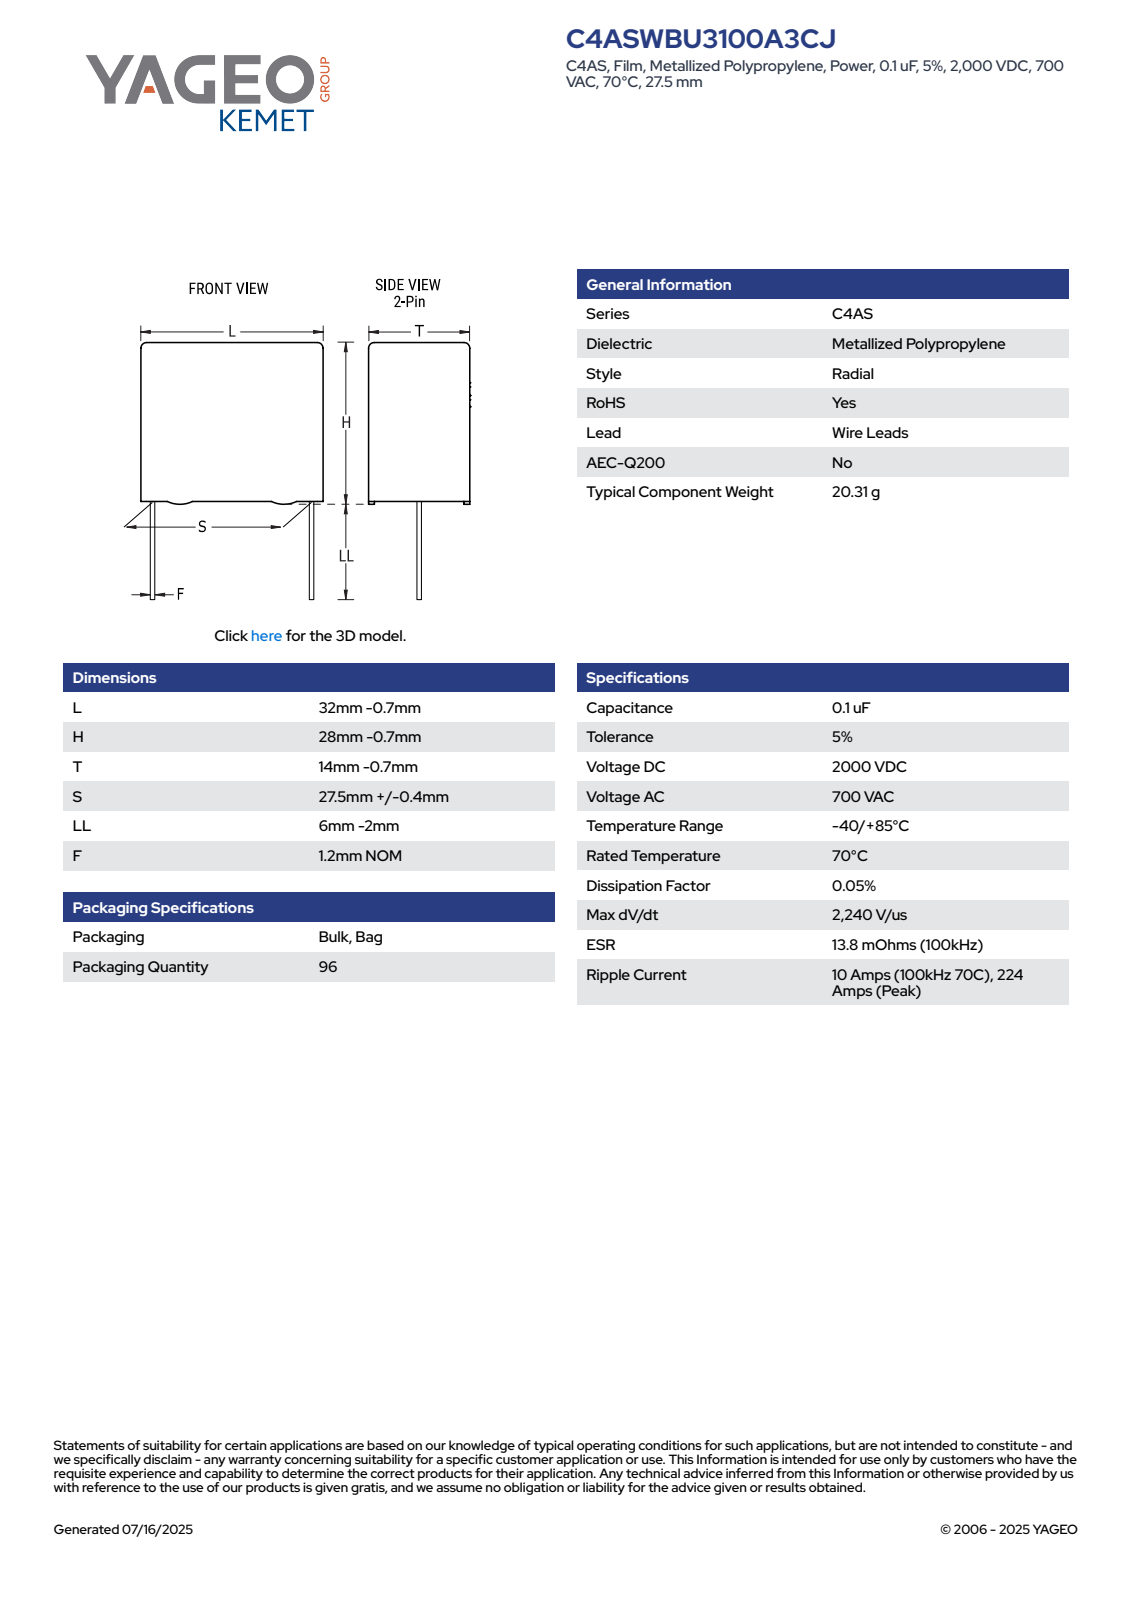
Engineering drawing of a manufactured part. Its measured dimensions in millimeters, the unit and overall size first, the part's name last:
Units: millimetres
Overall size (bounding box): 31.3 × 31.3 × 13.3
Round bosses / shafts (diameter × count): ⌀1.2 ×2
Partial cylindrical surfaces — rounded edges, fillets, slot ends (radius × count): R0.5 ×4
Main face-to-face distances: 13.3, 26.75, 31.3, 0.55, 27.3, 13.31, 0.76, 12.54, 0.77, 11.78
Volume: 11 151 mm³ · Surface area: 3 301 mm²
Bodies: 4 solids, 89 faces (81 planar, 8 cylindrical, 0 other)
Part name (STEP PRODUCT): CFP_RB_32X28X14_L31.3H27.3T13.3S27.5LL4F1.2
STEP written by: SolidWorks 2014 (AUTOMOTIVE_DESIGN)
